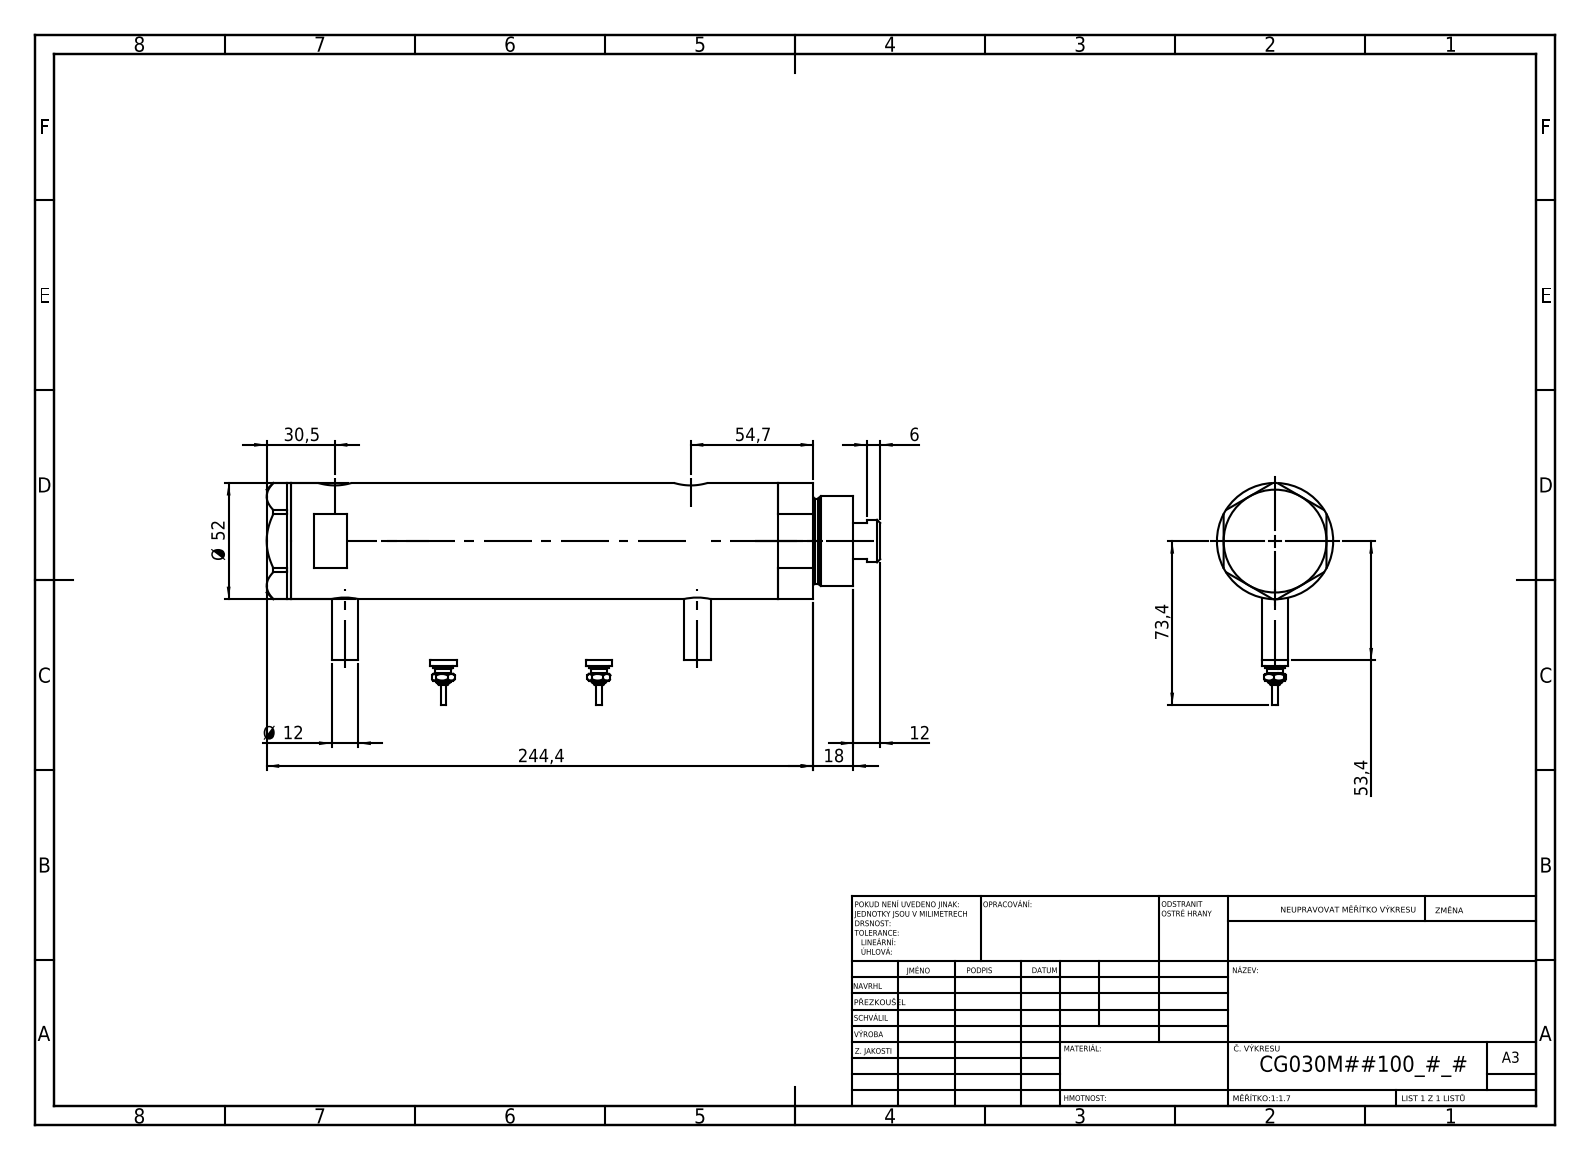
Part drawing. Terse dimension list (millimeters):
name: Switch; V270CG_FRONT; V270CG_MIDDLE; V270CG_BACK (+1 more)
written by: SolidWorks 2019 (CONFIG_CONTROL_DESIGN)
unit: mm
bodies: 6 solids, 226 faces (93 planar, 69 cylindrical, 64 other)
size: 274.4 × 99.4 × 52
volume: 504 580 mm³; area: 109 381 mm²
holes: 2× ⌀9.73, 2× ⌀12.5, 2× ⌀15, 1× ⌀6.5, 1× ⌀20, 1× ⌀21.5, 1× ⌀30, 1× ⌀33, 1× ⌀44
bosses: 4× ⌀12, 2× ⌀9, 2× ⌀7, 2× ⌀4.5, 2× ⌀2.5, 1× ⌀52, 1× ⌀40, 1× ⌀38
face distances: 181.5, 23.8, 157.7, 11, 34.8, 192.5, 46, 36.4, 228.9, 217.9
hole spacings: 2.9, 4.5, 154.7, 157.6, 159.2, 162.1
